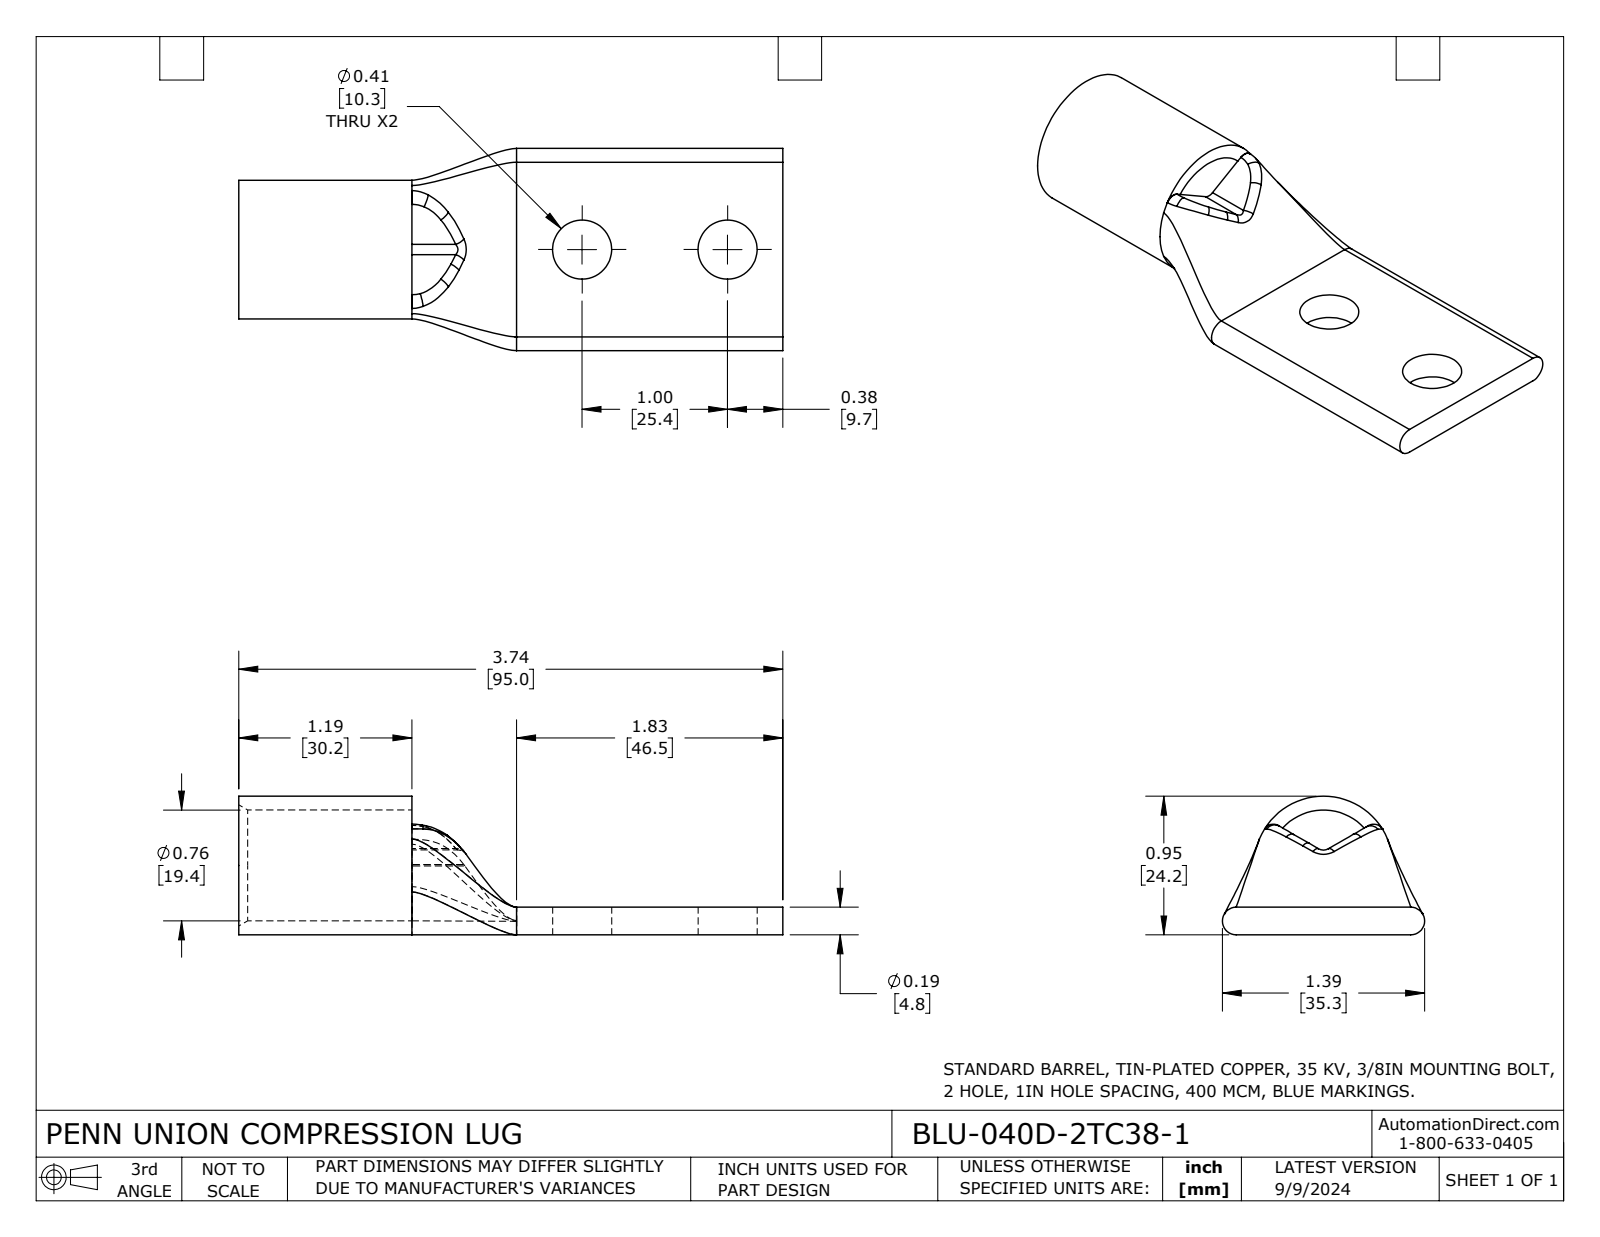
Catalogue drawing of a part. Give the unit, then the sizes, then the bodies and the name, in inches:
Units: inches
Overall size (bounding box): 3.74 × 1.39 × 0.953
Round holes (diameter × count): ⌀0.406 ×2, ⌀0.762 ×1
Round bosses / shafts (diameter × count): ⌀0.953 ×1
Partial cylindrical surfaces — rounded edges, fillets, slot ends (radius × count): R0.07 ×2, R0.095 ×2
Main face-to-face distances: 0.19, 3.74, 1.19, 2.55, 0.095, 1.91, 0.72, 1.83
Hole centre spacings: 1
Volume: 0.897 in³ · Surface area: 16.7 in²
Bodies: 1 solid, 44 faces (11 planar, 13 cylindrical, 20 other)
Part name (STEP PRODUCT): BLU-040D-2TC38-1
STEP written by: SolidWorks 2023 (CONFIG_CONTROL_DESIGN)
